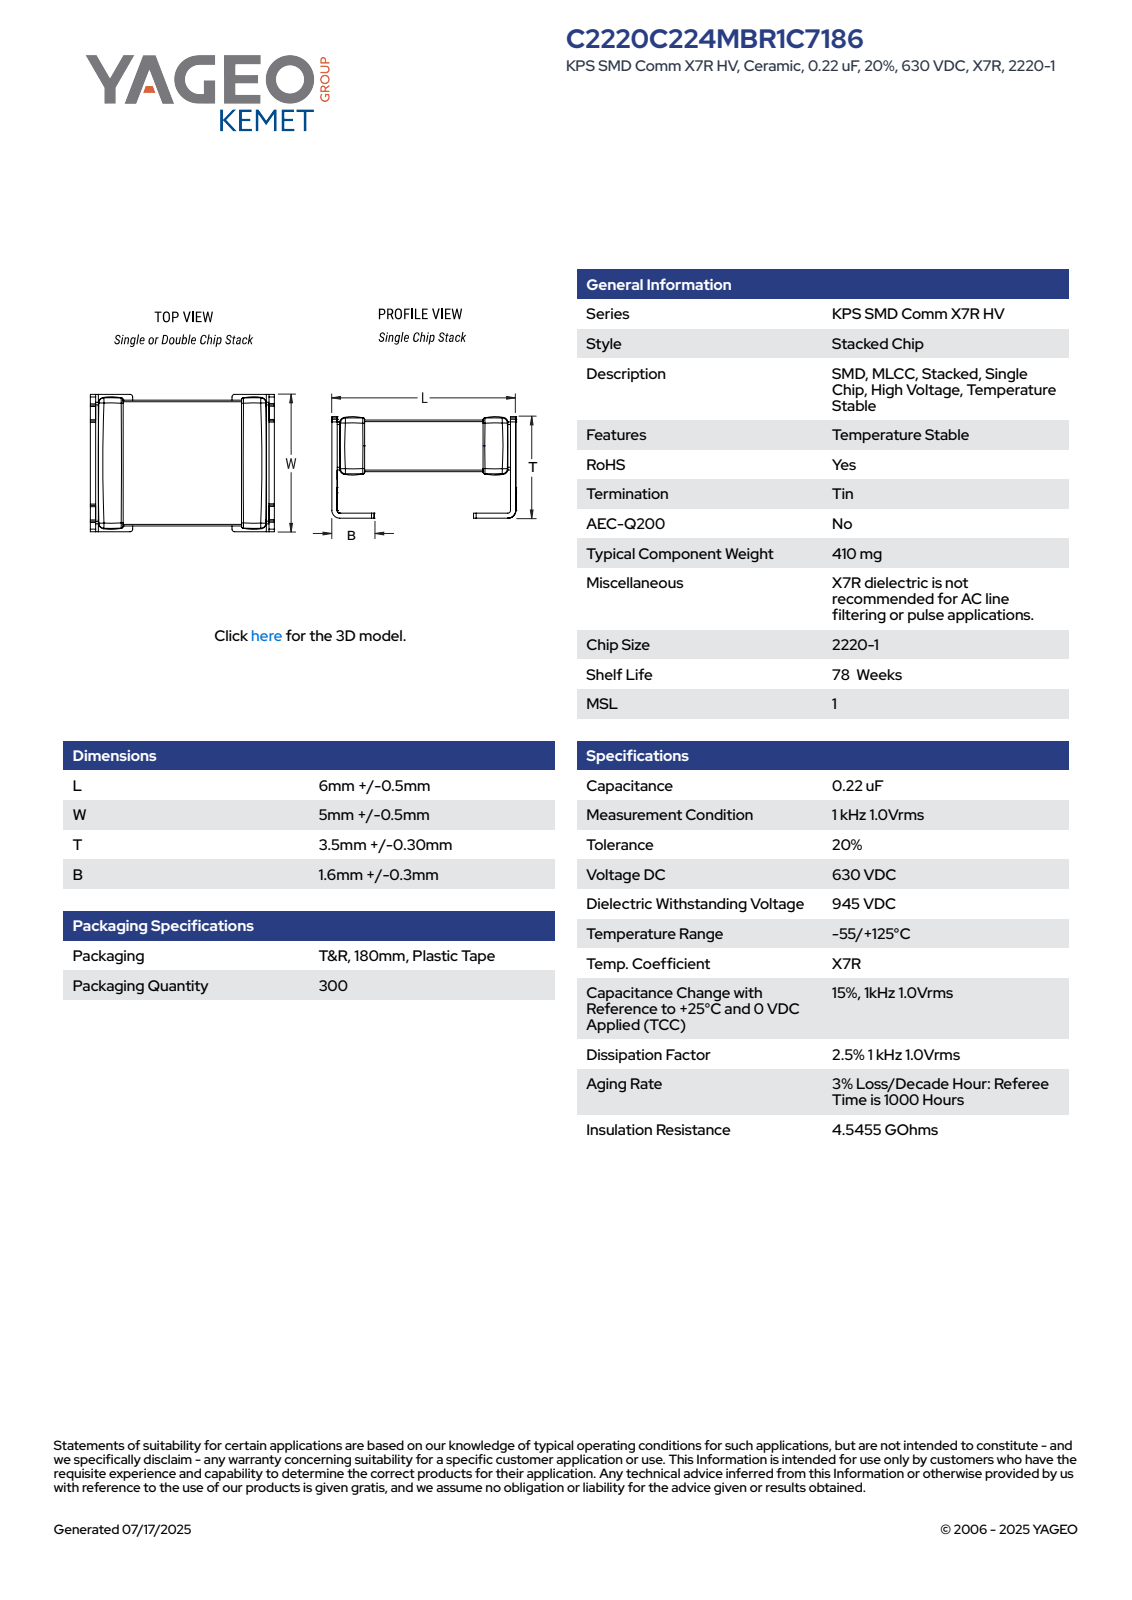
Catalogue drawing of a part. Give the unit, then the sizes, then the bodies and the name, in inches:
Units: inches
Overall size (bounding box): 0.256 × 0.217 × 0.15
Main face-to-face distances: 0.128, 0.13, 0.02, 0.15, 0.256, 0.146, 0.016, 0.217, 0.215, 0.148
Volume: 0.007 in³ · Surface area: 0.31 in²
Bodies: 4 solids, 169 faces (105 planar, 52 cylindrical, 12 other)
Part name (STEP PRODUCT): CCSS_S1_2220-1_L6.5W5.5T3.8B1.9
STEP written by: SolidWorks 2021 (AUTOMOTIVE_DESIGN)
